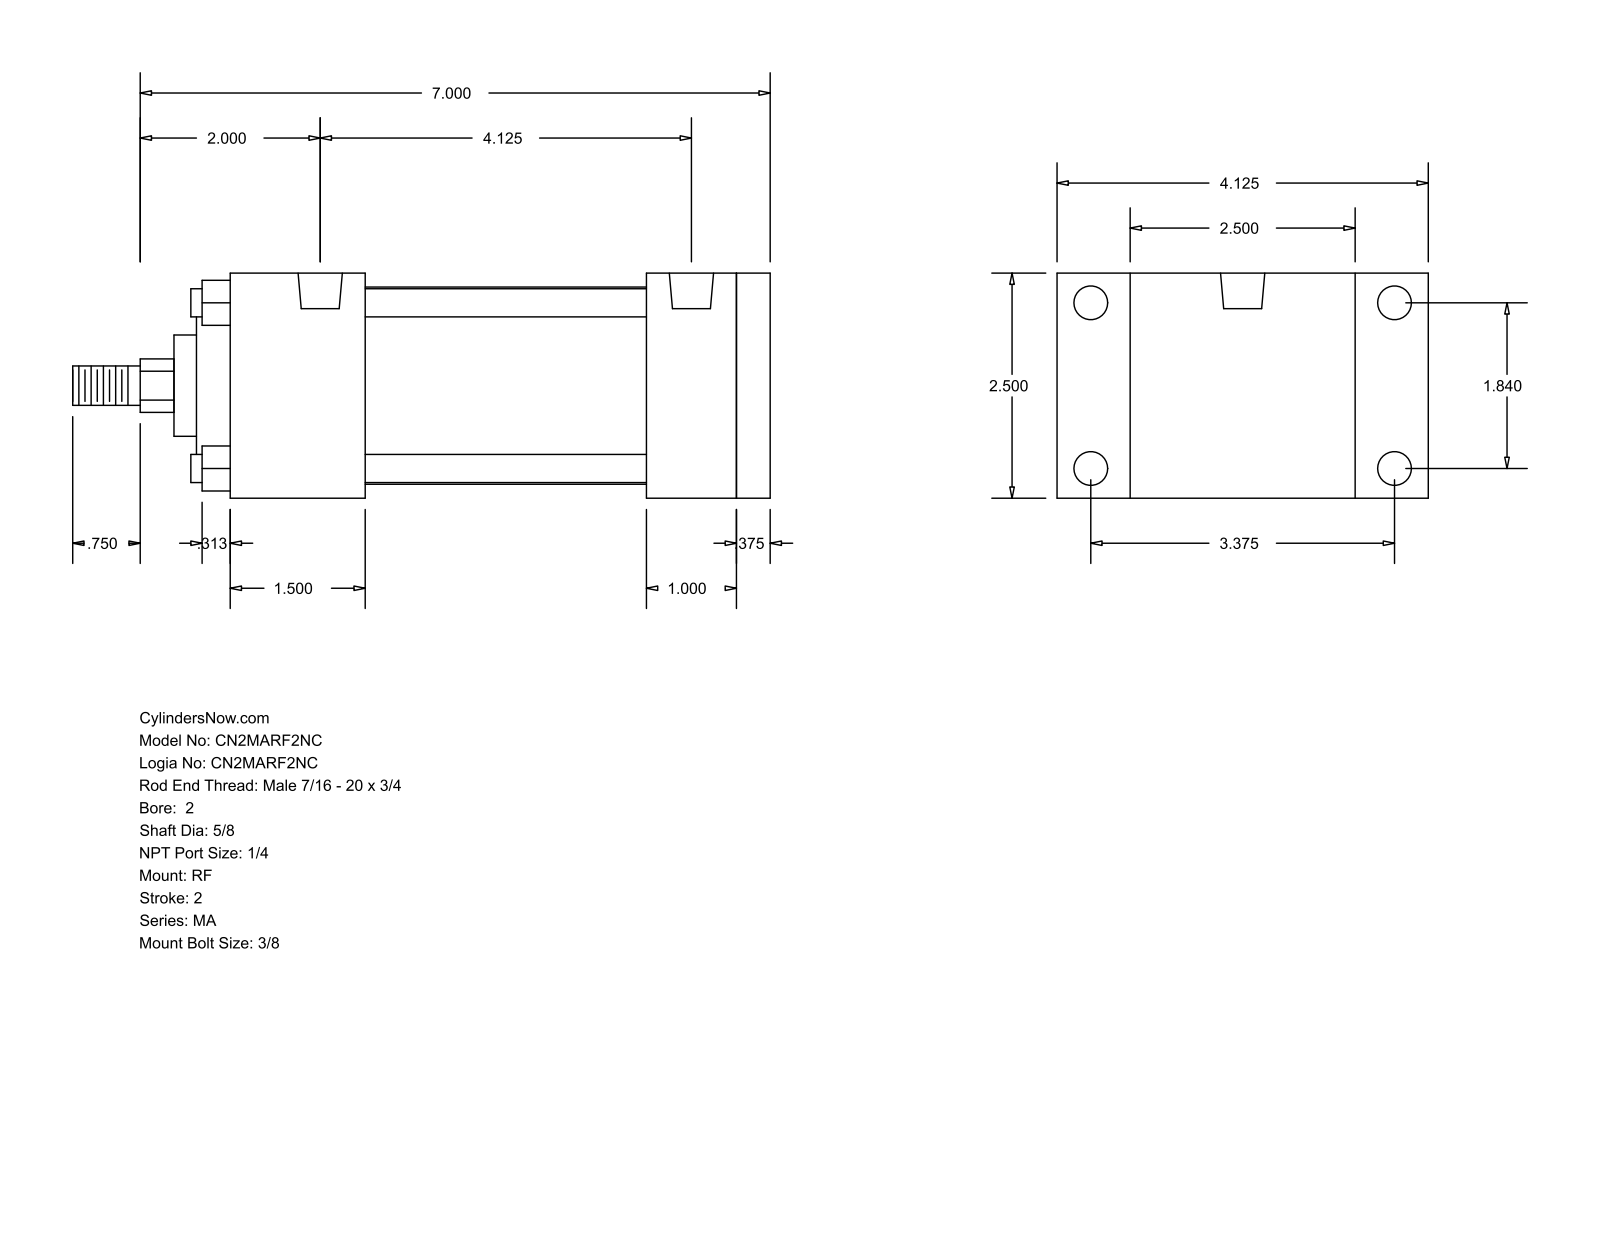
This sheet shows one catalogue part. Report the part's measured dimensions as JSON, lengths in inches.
{"part_name": "MA_RF__0200_0.625", "step_written_by": "GSSL Pune (CONFIG_CONTROL_DESIGN)", "units": "inches", "bodies": {"solids": 0, "faces": 94, "planar": 65, "cylindrical": 29, "other": 0}, "overall_size": [7.75, 4.125, 2.5], "round_holes": [[0.313, 4], [0.375, 4], [0.492, 2]], "round_bosses_or_shafts": [[0.313, 4], [2.19, 1], [2, 1], [1.125, 1], [0.625, 1], [0.437, 1]], "partial_cylinders_radius": [[0.297, 1]], "face_to_face_distances": [2.5, 0.375, 6, 4.125, 1, 1.5, 5.625, 4.5, 4.625, 3.125], "hole_center_spacings": [1.84, 3.375, 3.844, 4.125]}
